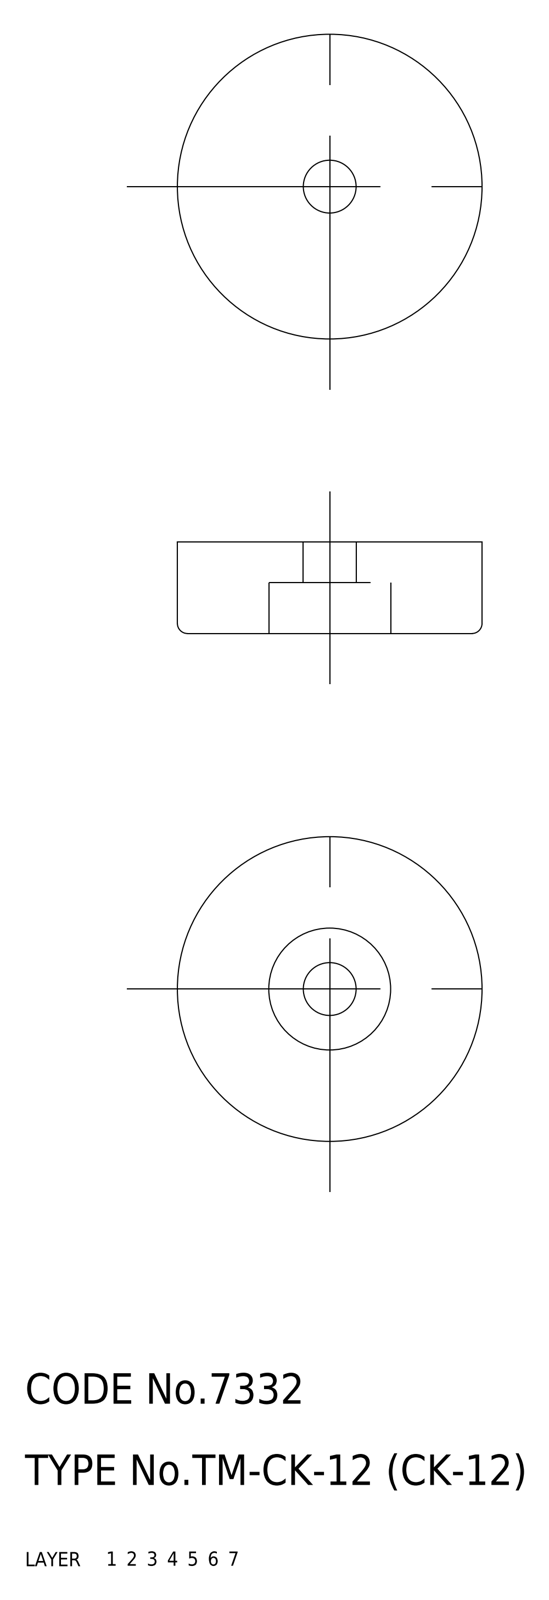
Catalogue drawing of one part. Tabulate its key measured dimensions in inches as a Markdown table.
| quantity | value |
| --- | --- |
| part name | washer; rubber foot; CK_12_1084_36 |
| STEP written by | CADfix (AUTOMOTIVE_DESIGN) |
| units | inches |
| bodies | 2 solids, 27 faces (0 planar, 0 cylindrical, 27 other) |
| overall size | 1.181 × 1.181 × 0.354 |
| volume | 0.319 in³ |
| surface area | 5.014 in² |
